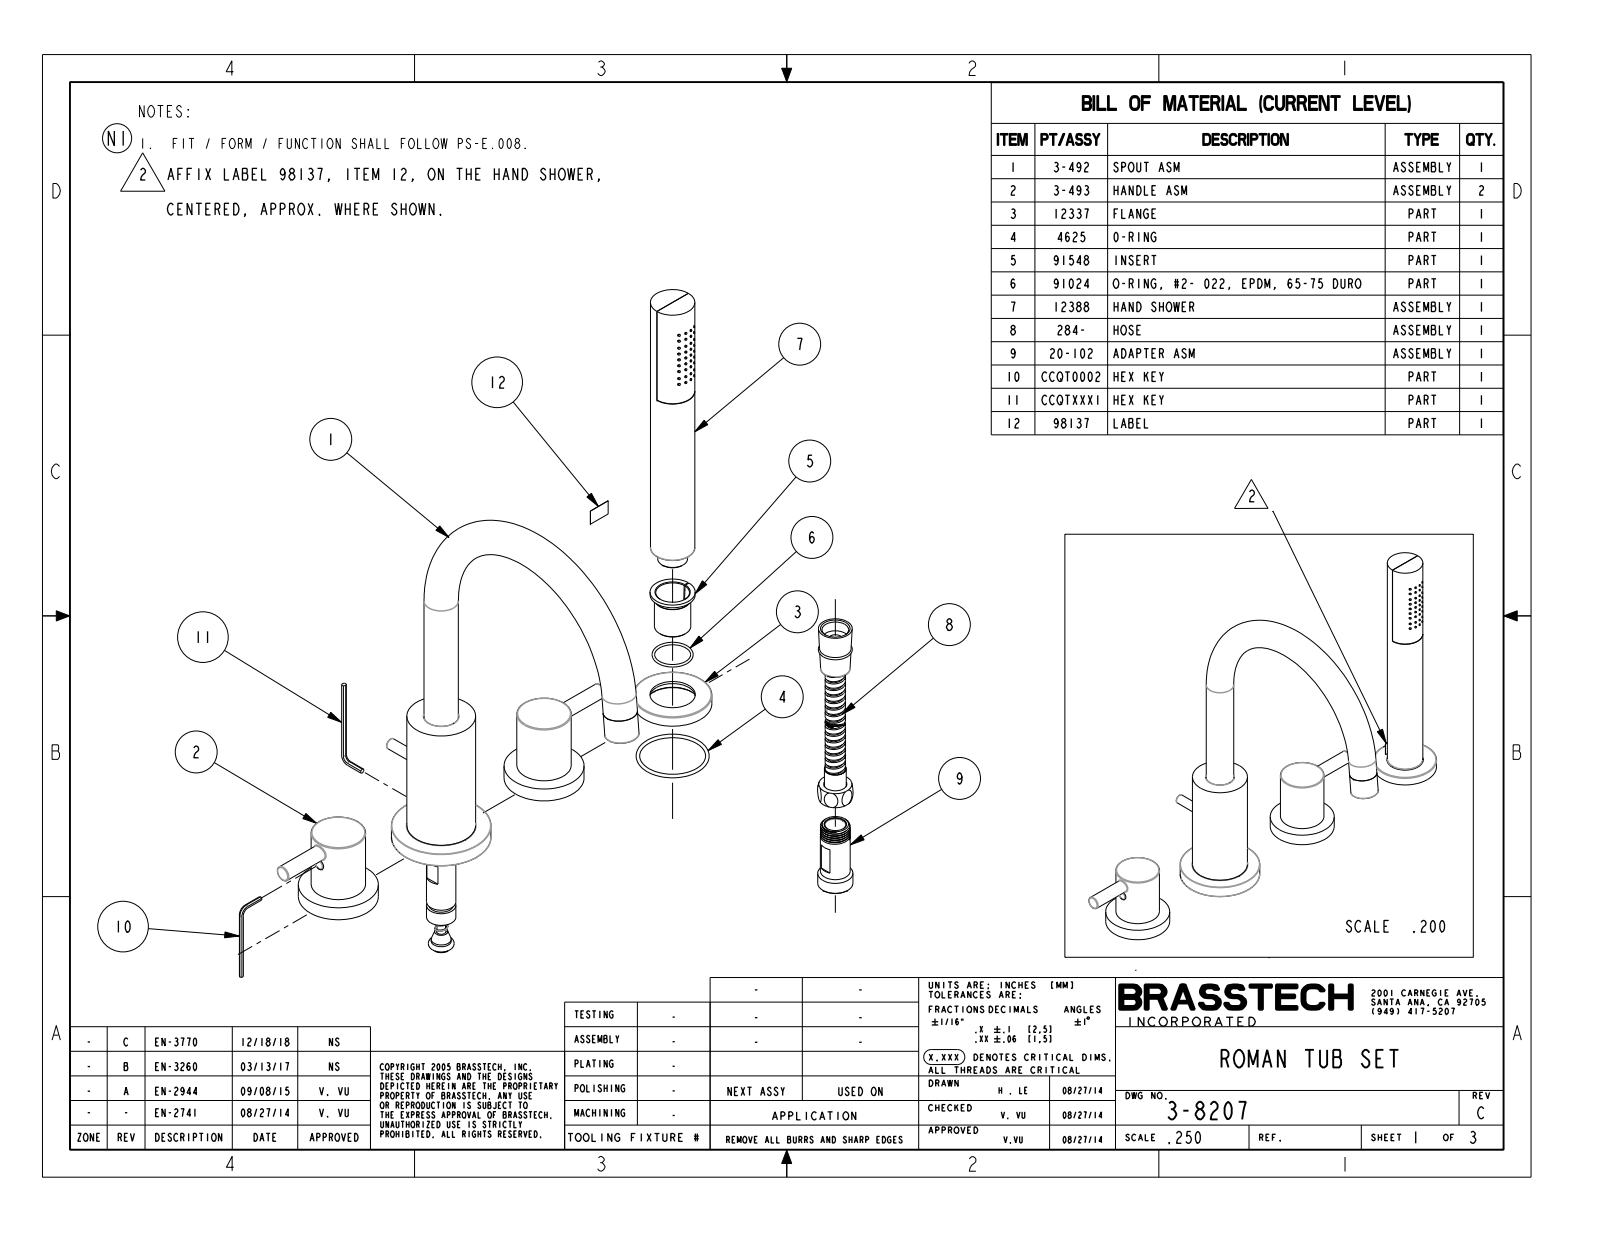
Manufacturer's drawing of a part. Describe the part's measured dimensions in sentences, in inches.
The part is named "CTST0224_1; CTDB0423_1_AF0; CTYB0522_1; ATBP0267-1_1 (+8 more)". Its 3-D file was written by "PRO/ENGINEER BY PARAMETRIC TECHNOLOGY CORPORATION, 2013150 (CONFIG_CONTROL_DESIGN)". It is 34 solids with 1140 faces: 305 planar, 537 cylindrical and 298 other. Overall it measures 16.244 by 11.886 by 9.466 inches. Its volume is 21.44 cubic inches and its surface area 332.5 square inches. Round holes: 2 of diameter 0.165, 2 of diameter 0.256, 2 of diameter 0.492, 2 of diameter 0.591, 2 of diameter 0.807, 2 of diameter 0.866, 2 of diameter 0.89, 2 of diameter 1, 2 of diameter 1.259, 2 of diameter 1.319, 2 of diameter 1.406, 2 of diameter 1.9. Round bosses or shafts: 36 of diameter 0.059, 2 of diameter 2.2, 2 of diameter 1.969, 2 of diameter 1.496, 2 of diameter 1.401, 2 of diameter 1.16, 2 of diameter 0.945, 2 of diameter 0.886. Partial cylindrical surfaces (rounded edges, fillets, slot ends): 12 of radius 0.016, 10 of radius 0.059, 8 of radius 0.039, 4 of radius 0.016, 3 of radius 0.118, 2 of radius 0.169, 2 of radius 0.176, 2 of radius 0.199. The main face-to-face distances are 0.4, 0.34, 0.06, 0.394, 0.054, 0.453, 0.114, 0.1, 0.094, 0.04. The hole center spacings are 4, 4.139, 0.52, 1.063, 5, 8, 9, 9.063.
